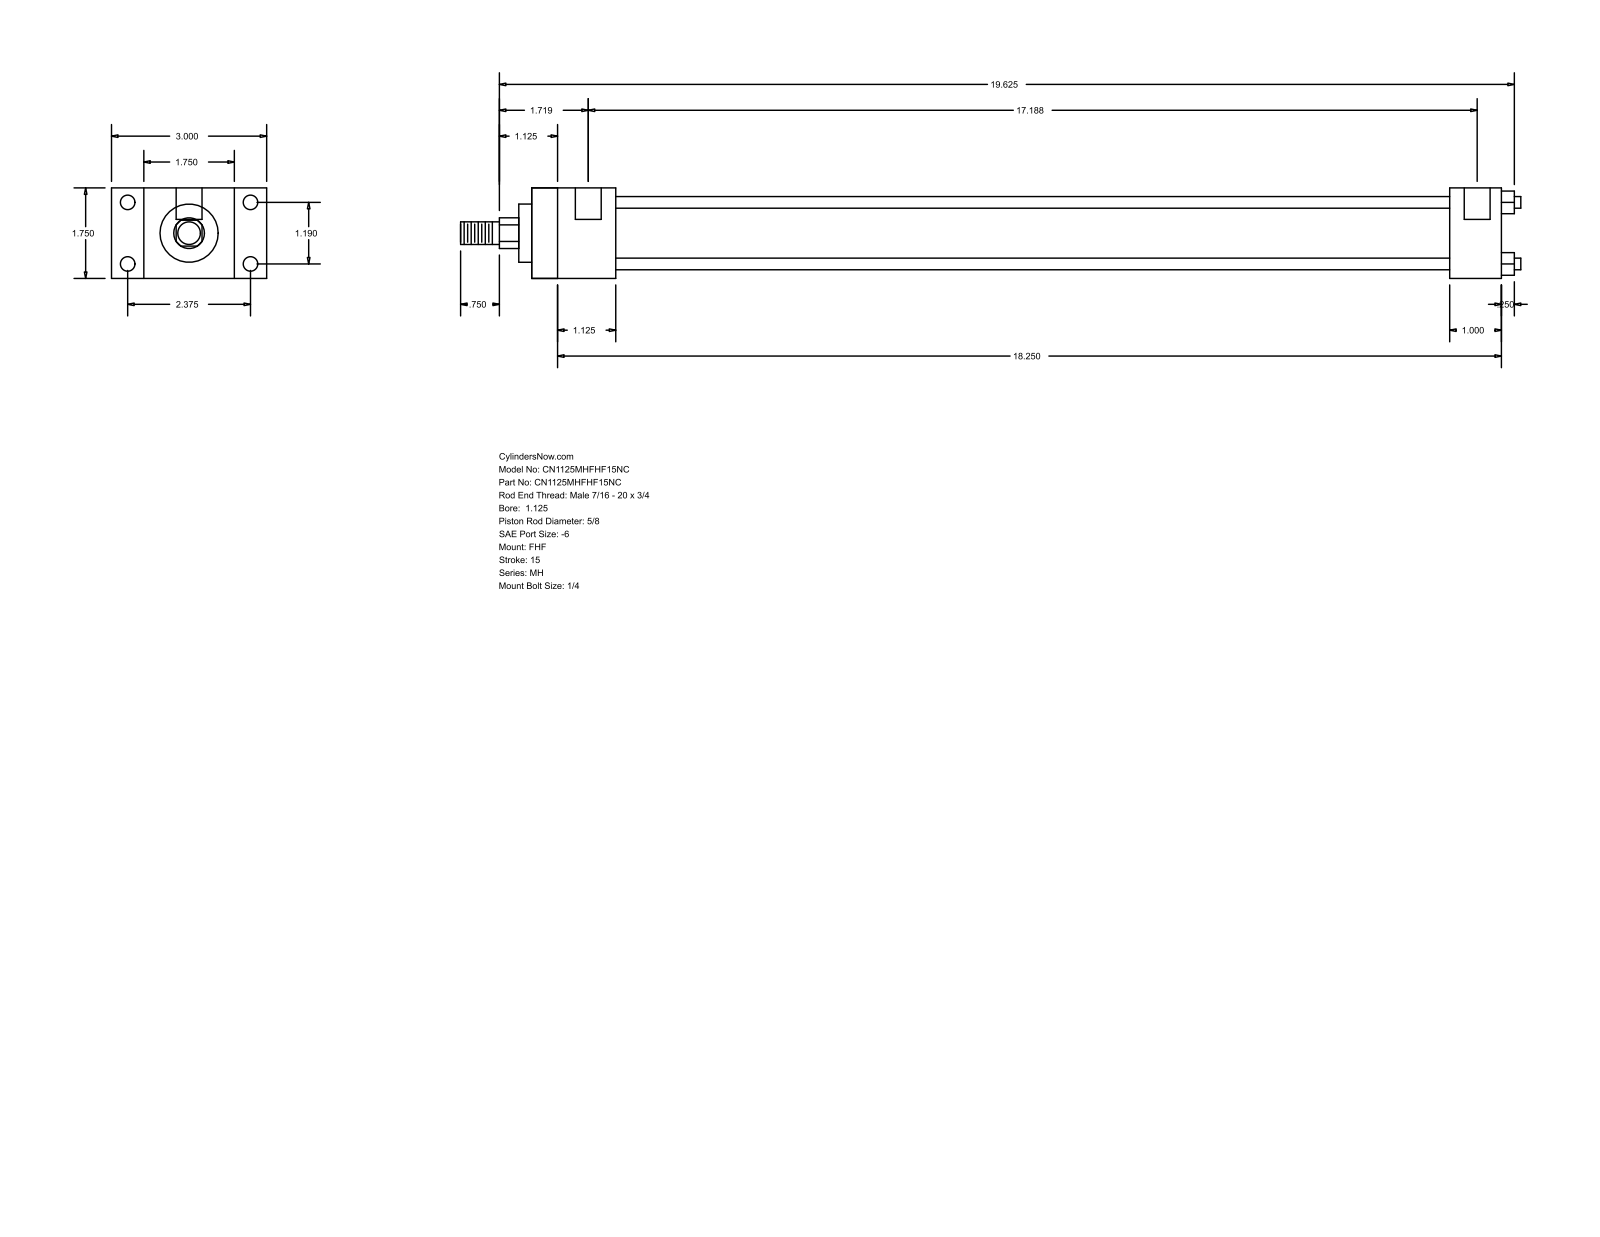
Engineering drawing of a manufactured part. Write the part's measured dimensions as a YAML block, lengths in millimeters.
part_name: "MH_FHF__0112_0.625"
step_written_by: "GSSL Pune (CONFIG_CONTROL_DESIGN)"
units: millimeters
bodies: {solids: 0, faces: 88, planar: 60, cylindrical: 28, other: 0}
overall_size: [520.7, 76.2, 44.45]
round_holes:
  - {diameter: 5.56, count: 4}
  - {diameter: 7.14, count: 4}
  - {diameter: 12.7, count: 2}
round_bosses_or_shafts:
  - {diameter: 5.71, count: 4}
  - {diameter: 34.92, count: 1}
  - {diameter: 28.57, count: 1}
  - {diameter: 15.88, count: 1}
  - {diameter: 11.11, count: 1}
partial_cylinders:
  - {radius: 7.54, count: 1}
face_to_face_distances: [44.46, 15.87, 60.33, 41.27, 76.2, 476.24, 434.97, 450.85, 409.58, 25.39]
hole_center_spacings: [30.22, 60.32, 67.47, 433.39, 3.17, 436.56]
